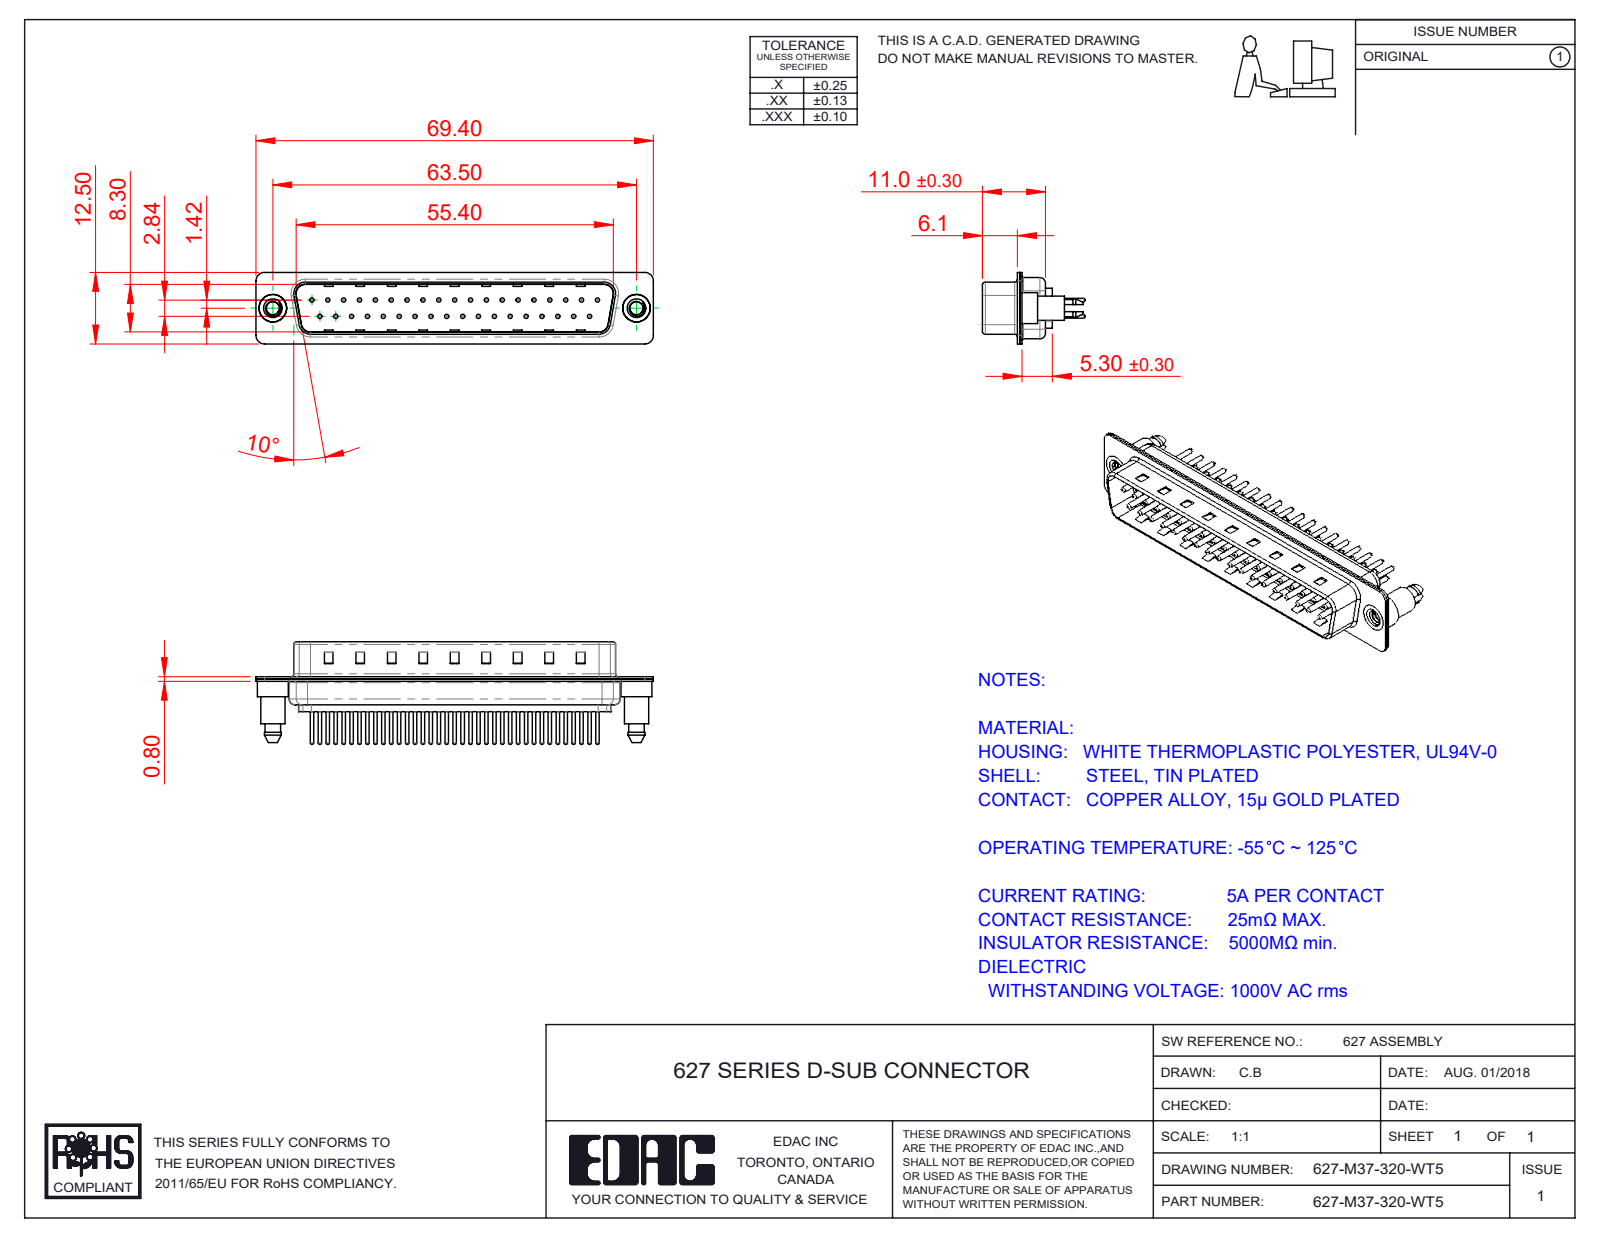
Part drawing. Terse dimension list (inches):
name: 627M Shell Front_37 Contacts; 627M Shell Rear_37 Contacts; 627M 4-40 Threaded Boardlock; 627M Contact Row 1_20 (+3 more)
written by: SolidWorks 2020 (CONFIG_CONTROL_DESIGN)
unit: in
bodies: 42 solids, 1831 faces (478 planar, 691 cylindrical, 662 other)
size: 2.732 × 0.705 × 0.492
volume: 0.238 in³; area: 14.88 in²
holes: 37× ⌀0.03, 37× ⌀0.063, 37× ⌀0.079, 2× ⌀0.089, 2× ⌀0.157, 2× ⌀0.189
bosses: 37× ⌀0.059, 37× ⌀0.024, 2× ⌀0.213, 2× ⌀0.193, 2× ⌀0.167
rounds: 18× R0.059, 12× R0.079, 10× R0.063, 8× R0.02, 4× R0.01, 4× R0.024, 4× R0.026, 4× R0.035
face distances: 0.016, 0.031, 0.374, 0.358, 0.343, 0.39, 0.047, 0.224, 0.03, 0.014
hole spacings: 0.109, 0.218, 0.124, 0.327, 0.436, 0.545, 0.654, 0.763
